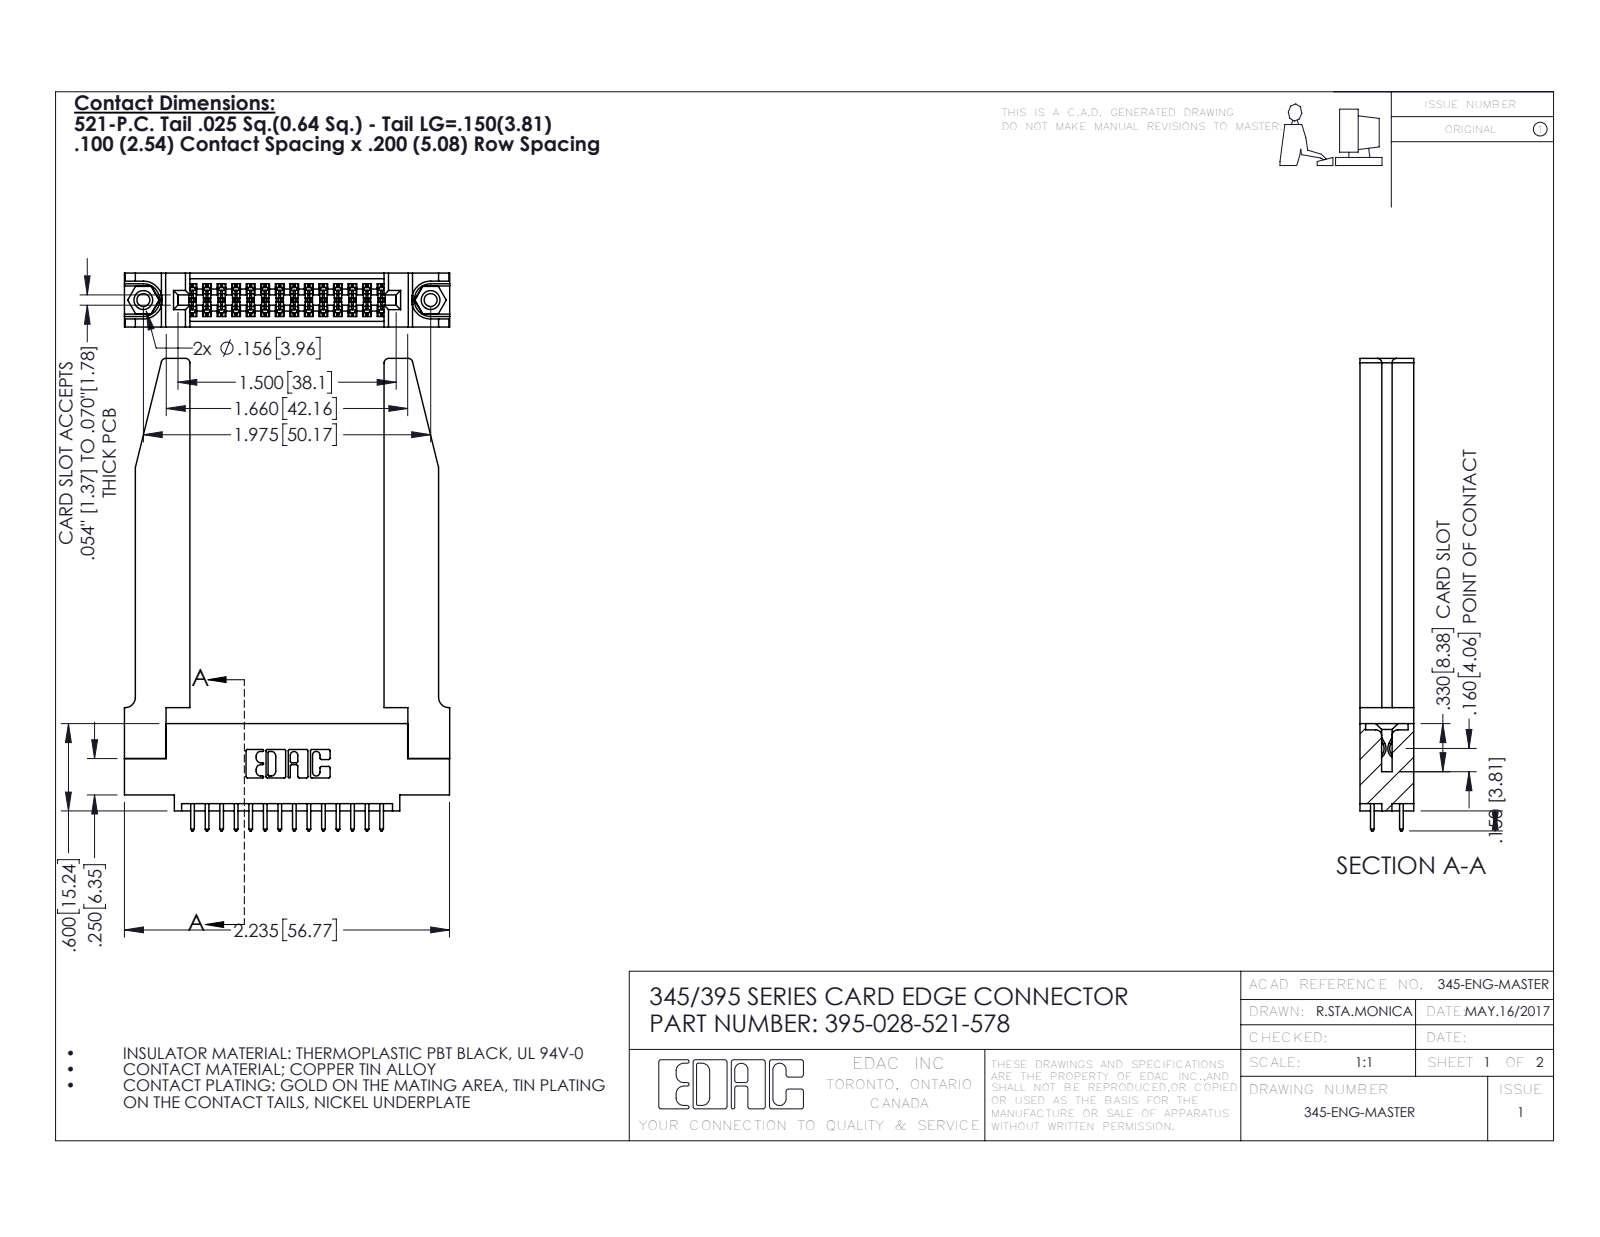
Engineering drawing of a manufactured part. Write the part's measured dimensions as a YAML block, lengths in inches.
part_name: "345-250-001_345-250-001-102; 345-220-078_345-220-078; 345-292-001_345-293-121; 395-028-521-578 (+1 more)"
step_written_by: "SolidWorks 2016 (CONFIG_CONTROL_DESIGN)"
units: inches
bodies: {solids: 33, faces: 1764, planar: 1150, cylindrical: 562, other: 52}
overall_size: [3.247, 2.236, 0.37]
volume: 0.79
surface_area: 21.64
round_holes:
  - {diameter: 0.089, count: 2}
  - {diameter: 0.125, count: 2}
  - {diameter: 0.156, count: 2}
  - {diameter: 0.064, count: 1}
round_bosses_or_shafts:
  - {diameter: 0.155, count: 2}
partial_cylinders:
  - {radius: 0.006, count: 42}
  - {radius: 0.01, count: 28}
  - {radius: 0.01, count: 22}
  - {radius: 0.03, count: 8}
  - {radius: 0.007, count: 6}
  - {radius: 0.031, count: 6}
  - {radius: 0.026, count: 3}
  - {radius: 0.014, count: 2}
face_to_face_distances: [0.37, 0.072, 0.298, 0.2, 0.148, 0.15, 0.098, 0.272, 0.025, 0.22]
hole_center_spacings: [0.27, 1.742, 1.975]
